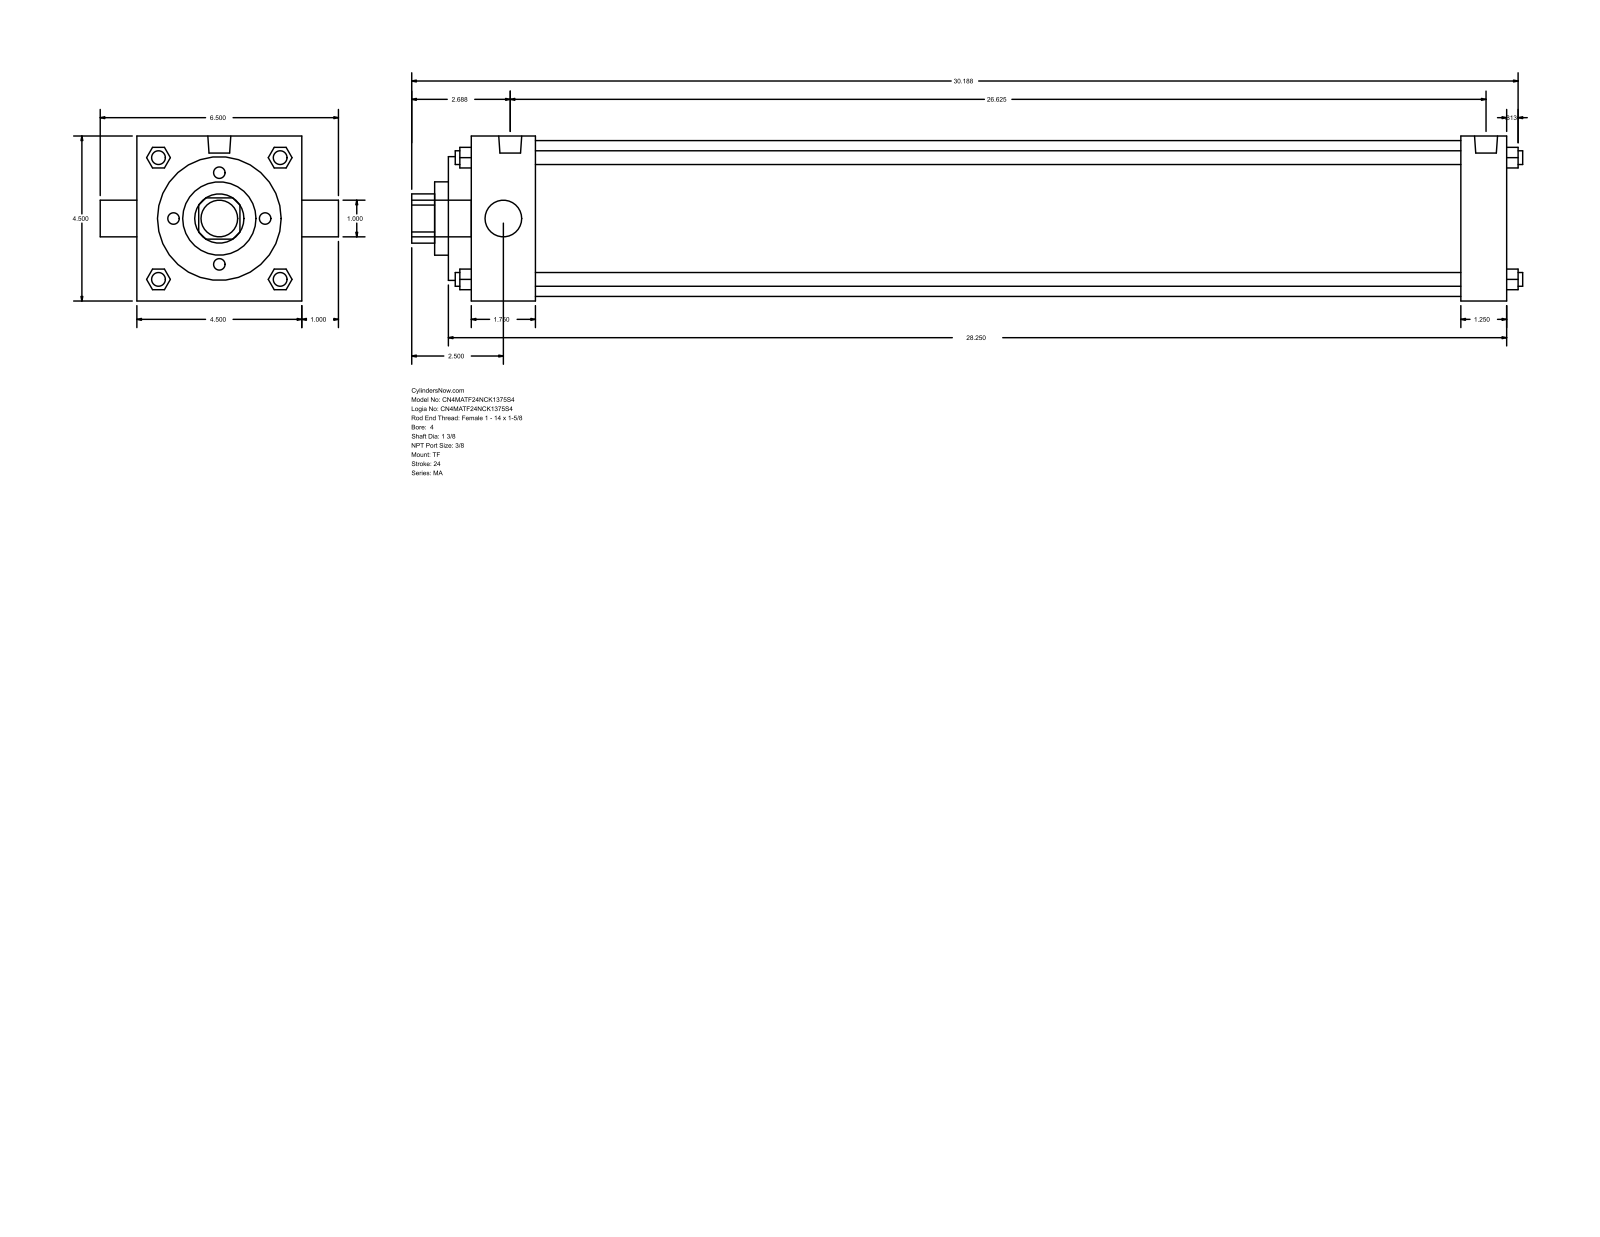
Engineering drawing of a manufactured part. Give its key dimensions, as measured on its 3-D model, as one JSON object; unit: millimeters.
{"part_name": "MA_TF__0400_1.375", "step_written_by": "GSSL Pune (CONFIG_CONTROL_DESIGN)", "units": "millimeters", "bodies": {"solids": 0, "faces": 122, "planar": 93, "cylindrical": 29, "other": 0}, "overall_size": [769.94, 165.1, 114.3], "round_holes": [[25.4, 1], [34.92, 1], [50.8, 1], [85.72, 1], [107.95, 1]], "round_bosses_or_shafts": [[9.53, 4], [11.11, 3], [15.93, 2], [25.4, 1]], "partial_cylinders_radius": [[17.06, 1]], "face_to_face_distances": [114.3, 717.56, 15.87, 733.43, 701.68, 685.81, 31.75, 60.32, 44.45, 641.36]}
